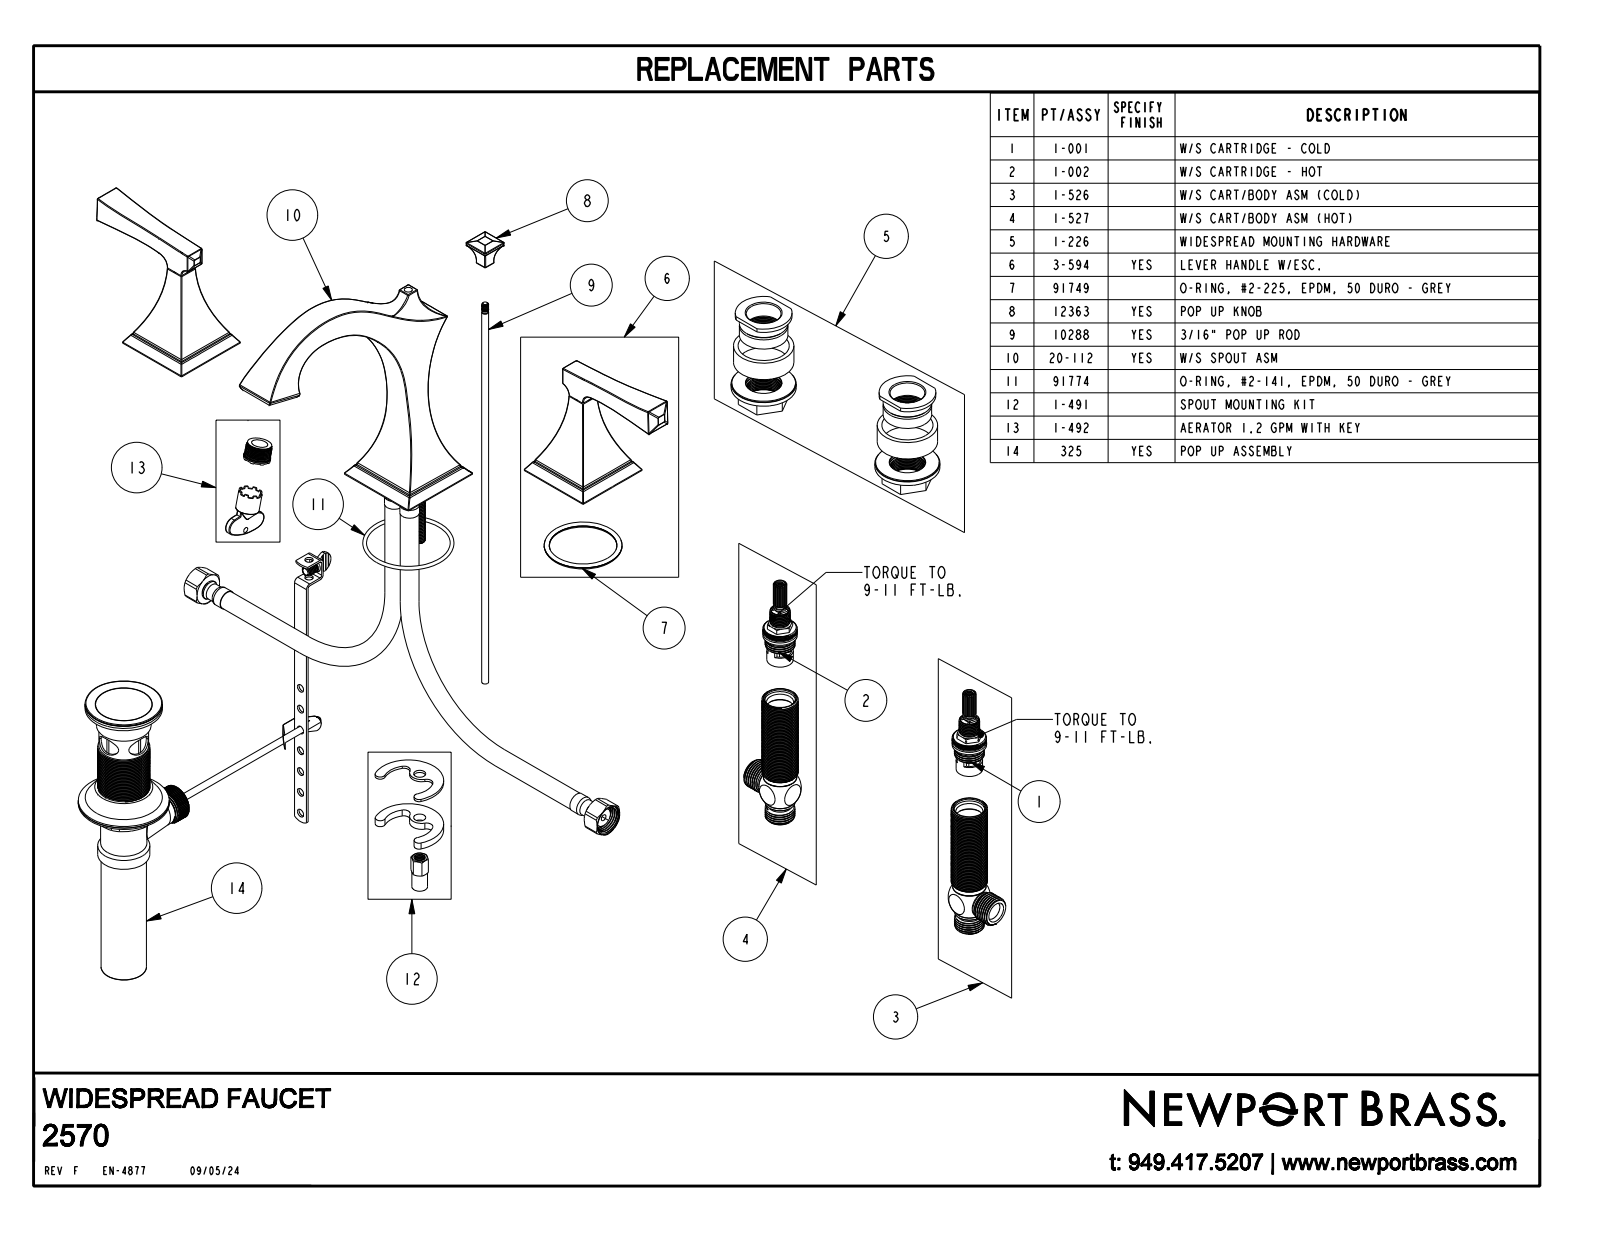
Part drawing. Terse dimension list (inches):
name: 2570
written by: CREO PARAMETRIC BY PTC INC, 2018400 (CONFIG_CONTROL_DESIGN)
unit: in
bodies: 3 solids, 534 faces (45 planar, 112 cylindrical, 377 other)
size: 14.104 × 7.23 × 7.09
volume: 23.9 in³; area: 113.2 in²
bosses: 2× ⌀0.4
rounds: 71× R0.02, 20× R0.06, 4× R0.04, 4× R0.2, 2× R0.025, 2× R0.09, 2× R34.711, 1× R0.09
face distances: 0.56, 2.5, 2.531, 0.031, 5.607, 6.946, 4.447, 4.416, 0.1, 0.659
